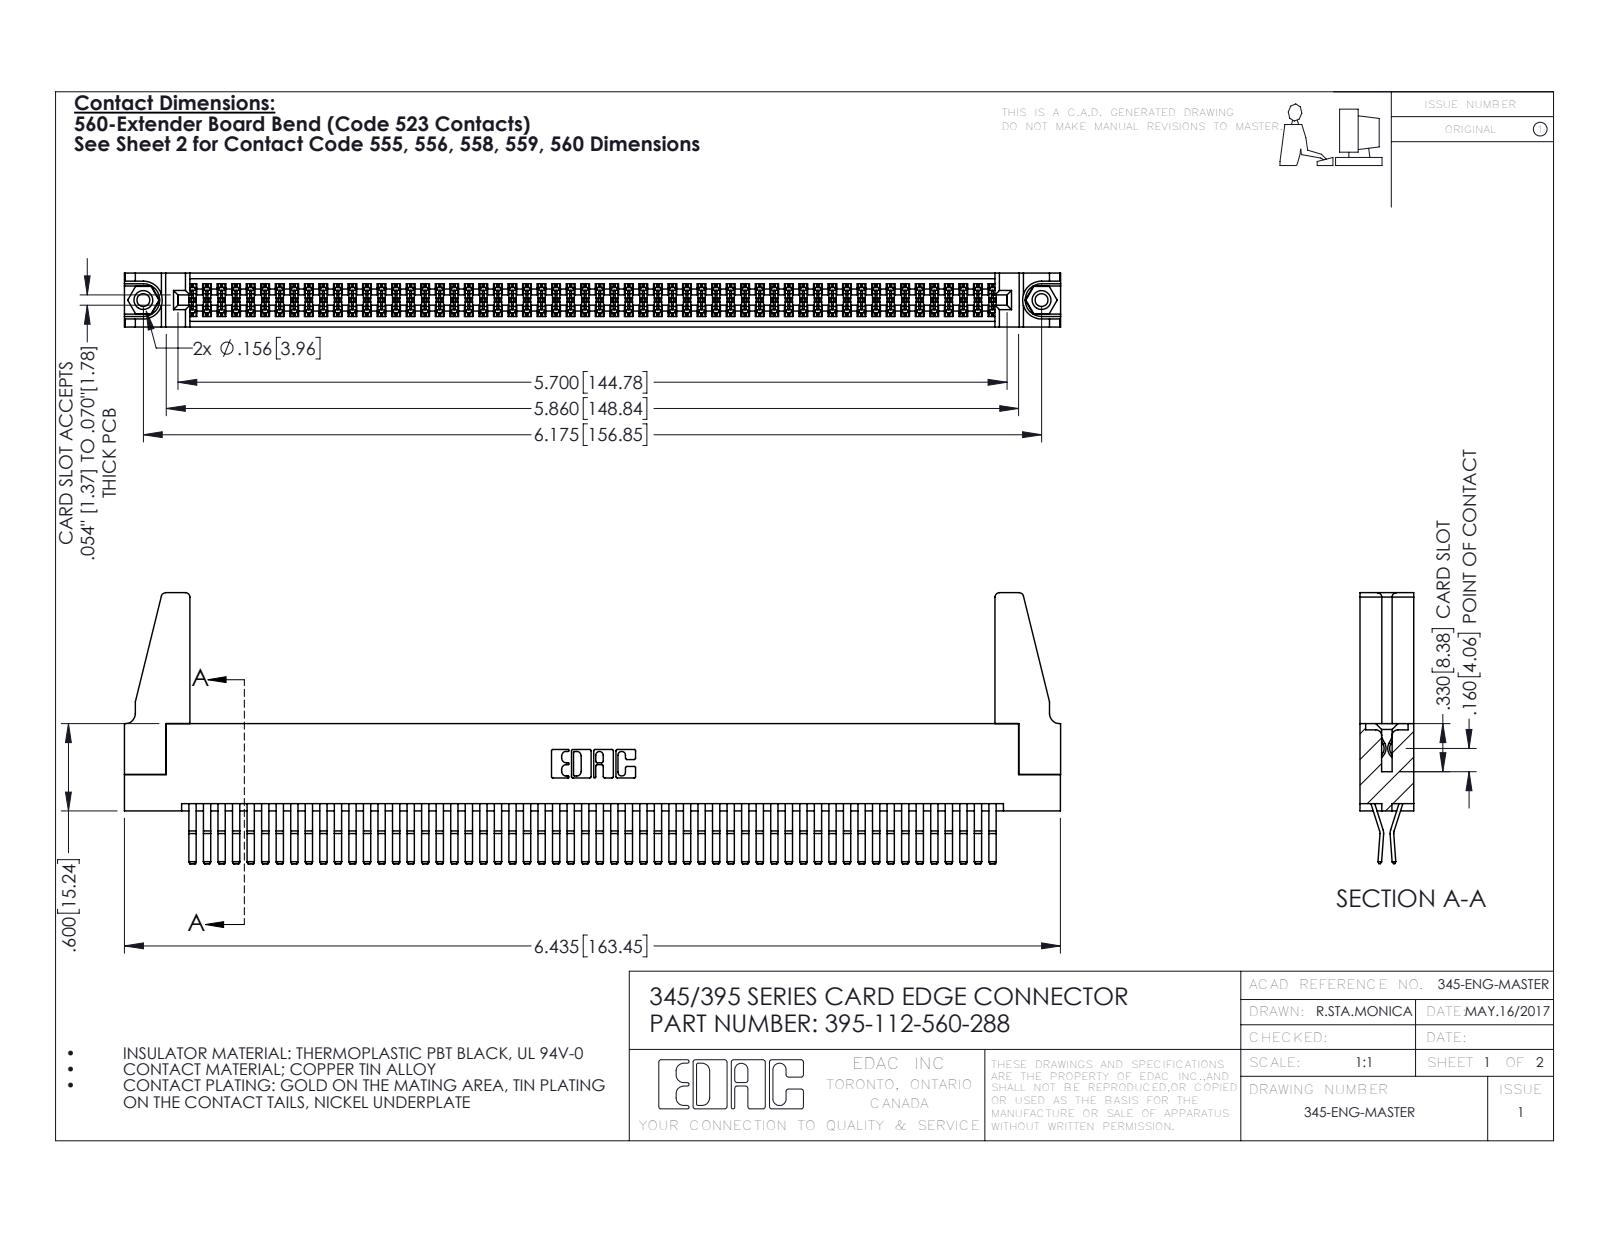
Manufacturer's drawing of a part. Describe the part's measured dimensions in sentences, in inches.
The part is named "395-112-560-288; 345-250-001_345-250-001-102; 345 Part_Flush Mounting Lugs - 0.156 Dia-TH; 345-292-001_560 Tail (+1 more)". Its 3-D file was written by "SolidWorks 2016 (CONFIG_CONTROL_DESIGN)". It is 117 solids with 6074 faces: 3848 planar, 2210 cylindrical and 16 other. Overall it measures 6.436 by 1.862 by 0.37 inches. Its volume is 1.22 cubic inches and its surface area 46.55 square inches. Round holes: 2 of diameter 0.089, 2 of diameter 0.125, 2 of diameter 0.156, 1 of diameter 0.064. Round bosses or shafts: 2 of diameter 0.155. Partial cylindrical surfaces (rounded edges, fillets, slot ends): 168 of radius 0.006, 22 of radius 0.01, 8 of radius 0.03, 6 of radius 0.007, 6 of radius 0.031, 3 of radius 0.026, 2 of radius 0.01, 2 of radius 0.014. The main face-to-face distances are 0.072, 0.298, 0.025, 0.37, 0.2, 0.098, 0.272, 0.225, 0.175, 0.149. The hole center spacings are 0.27, 5.939, 6.175.
